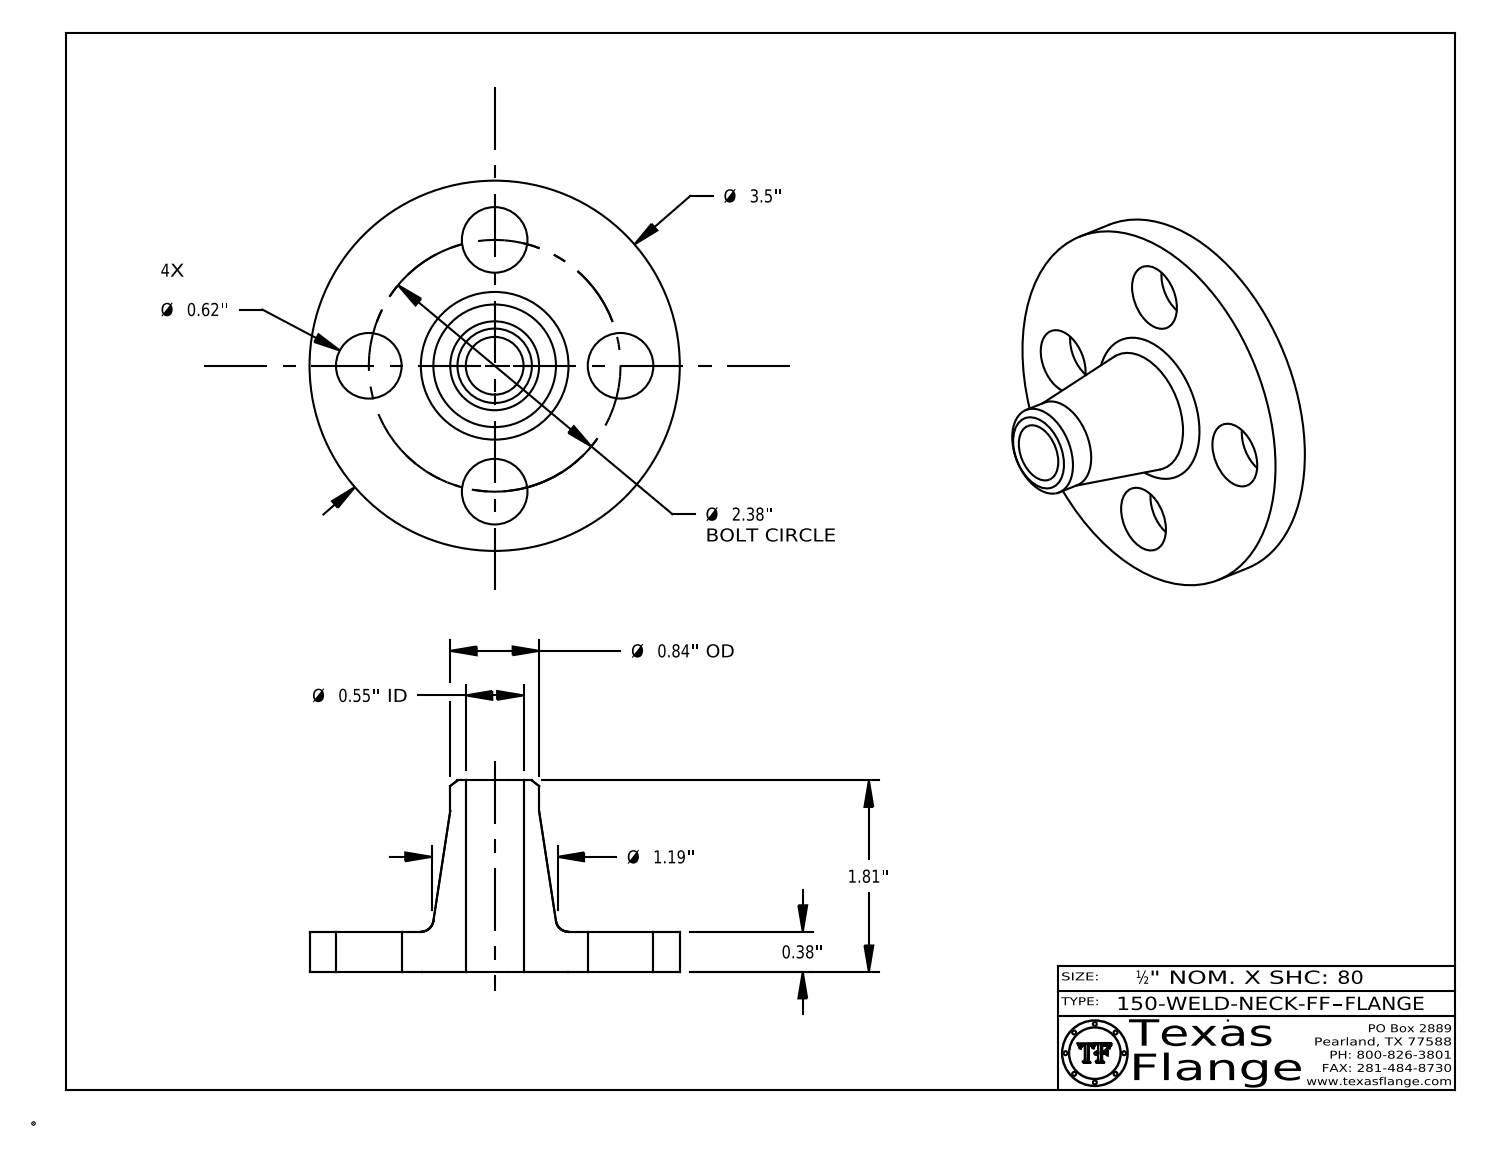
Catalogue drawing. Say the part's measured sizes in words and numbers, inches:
The part is named "150-WELD-NECK-FF". Its 3-D file was written by "CATIA V5 STEP AP214 (AUTOMOTIVE_DESIGN)". It is 1 solid with 409 faces: 369 planar, 34 cylindrical and 6 other. Overall it measures 3.5 by 3.5 by 1.81 inches. Its volume is 3.869 cubic inches and its surface area 30.36 square inches. Round holes: 4 of diameter 0.62, 1 of diameter 0.495, 1 of diameter 0.546. Round bosses or shafts: 8 of diameter 0.03, 1 of diameter 3.5, 1 of diameter 0.84, 1 of diameter 0.39. The main face-to-face distances are 0.38, 1.81, 1.43, 0.365, 0.015, 1.445, 0.148, 0.145, 0.027, 0.096. The hole center spacings are 1.19, 1.683, 0.911, 2.199, 2.38, 1.19.
